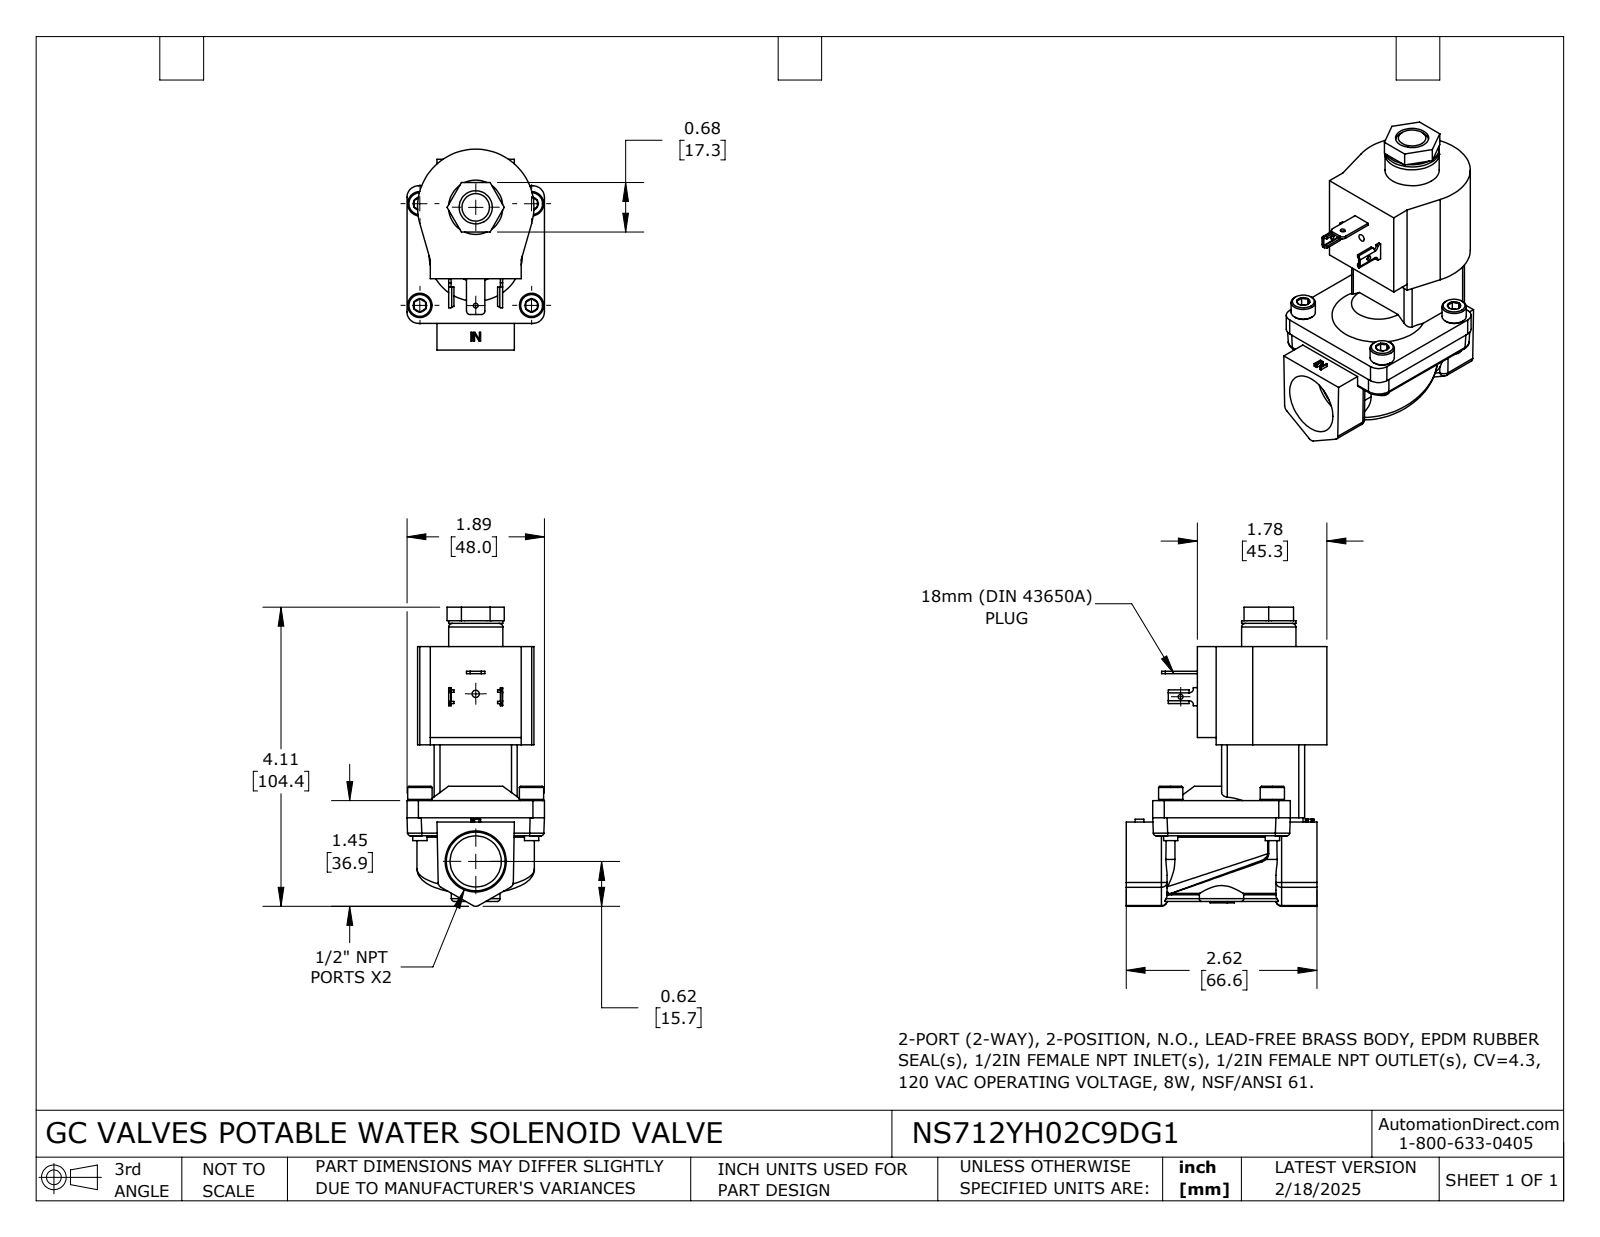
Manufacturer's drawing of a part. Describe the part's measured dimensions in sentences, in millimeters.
The part is named "NS712YH02C9DG1". Its 3-D file was written by "SolidWorks 2024 (CONFIG_CONTROL_DESIGN)". It is 2 solids with 501 faces: 276 planar, 118 cylindrical and 107 other. Overall it measures 104.4 by 70.12 by 48 millimeters. Its volume is 130 218 cubic millimeters and its surface area 30 112 square millimeters. Round holes: 1 of diameter 1.68, 1 of diameter 1.7, 1 of diameter 2.53, 1 of diameter 11.58, 1 of diameter 17.86, 1 of diameter 30.48. Round bosses or shafts: 4 of diameter 8.5, 4 of diameter 5, 1 of diameter 18.95. Partial cylindrical surfaces (rounded edges, fillets, slot ends): 15 of radius 2, 6 of radius 0.5, 6 of radius 1, 4 of radius 0.15, 4 of radius 1.04, 4 of radius 4, 4 of radius 5, 2 of radius 1.27. The main face-to-face distances are 53.79, 29, 19.5, 34.29, 33.3, 37.44, 9.5, 27, 38.5, 12.3. The hole center spacings are 34.29, 58.5.
